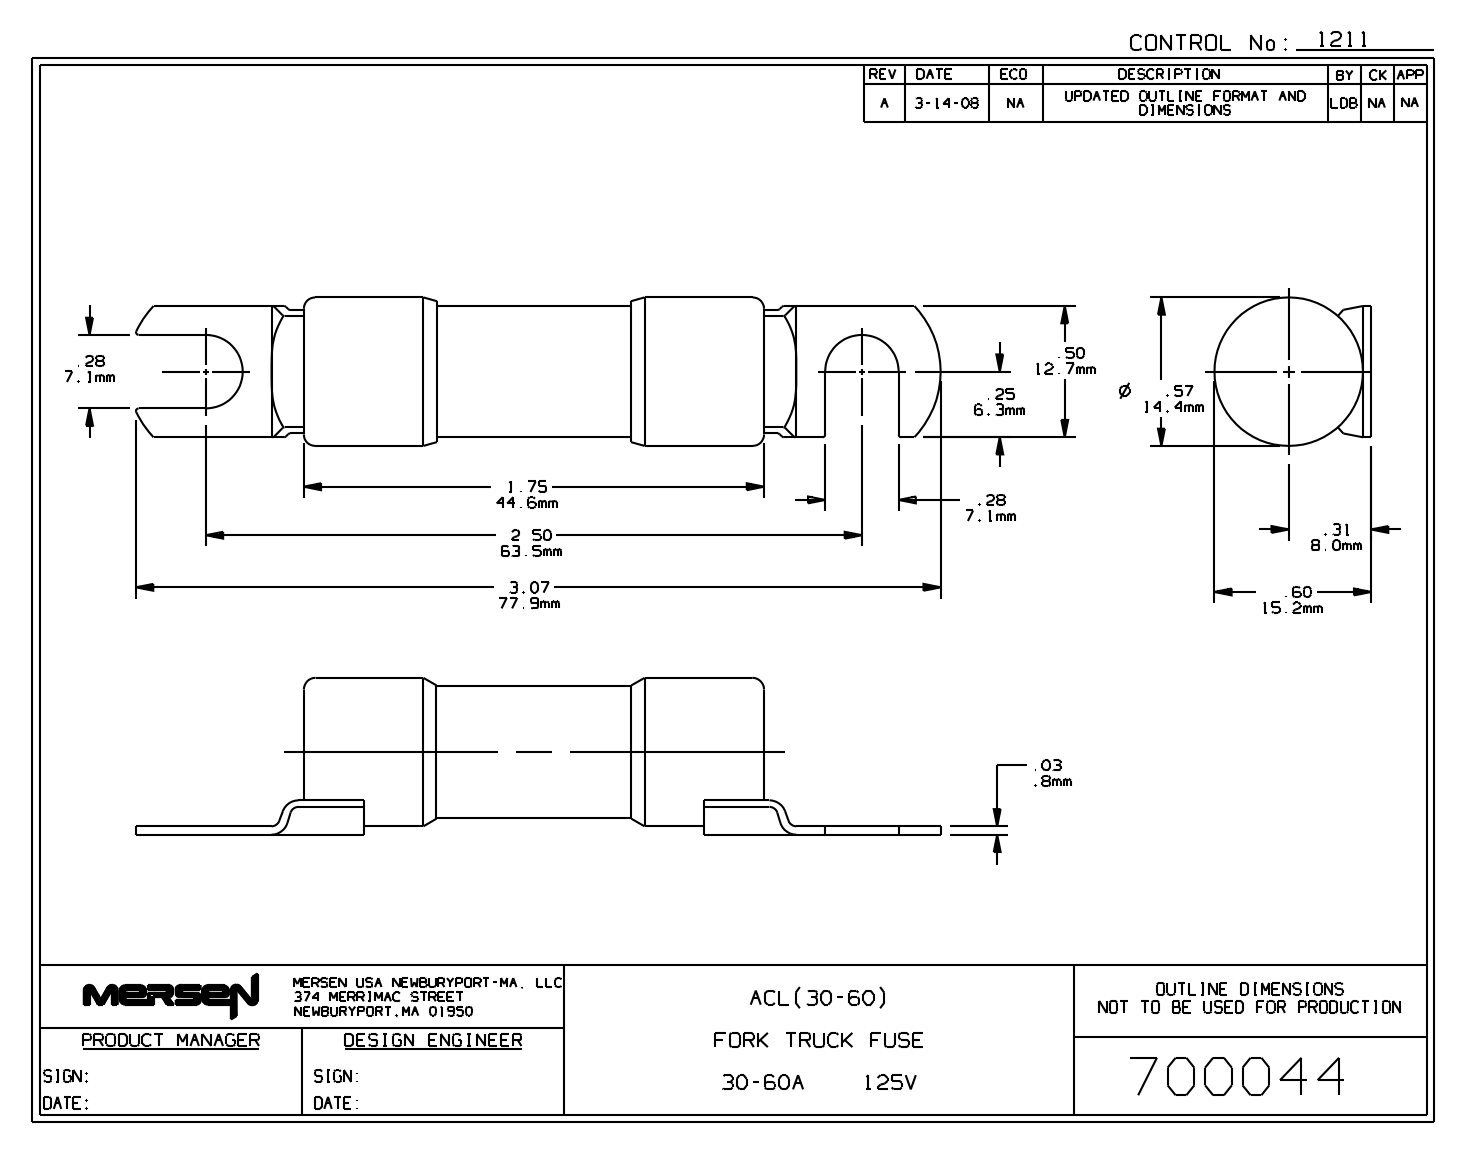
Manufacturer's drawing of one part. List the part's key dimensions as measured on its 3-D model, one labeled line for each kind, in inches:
Part name (STEP PRODUCT): 700044revA
STEP written by: SolidWorks 2017 (AUTOMOTIVE_DESIGN)
Units: inches
Bodies: 5 solids, 103 faces (29 planar, 30 cylindrical, 44 other)
Overall size (bounding box): 3.067 × 0.605 × 0.566
Volume: 0.217 in³ · Surface area: 10.53 in²
Round holes (diameter × count): ⌀0.375 ×1, ⌀0.511 ×1
Round bosses / shafts (diameter × count): ⌀0.566 ×1, ⌀0.496 ×1
Partial cylindrical surfaces — rounded edges, fillets, slot ends (radius × count): R0.01 ×4, R0.129 ×2, R0.36 ×2, R0.031 ×1, R0.062 ×1, R0.288 ×1, R0.319 ×1, R0.319 ×1
Main face-to-face distances: 0.028, 1.728, 0.032, 1.755, 1.7, 0.031, 0.043, 1.713, 0.015, 1.685
